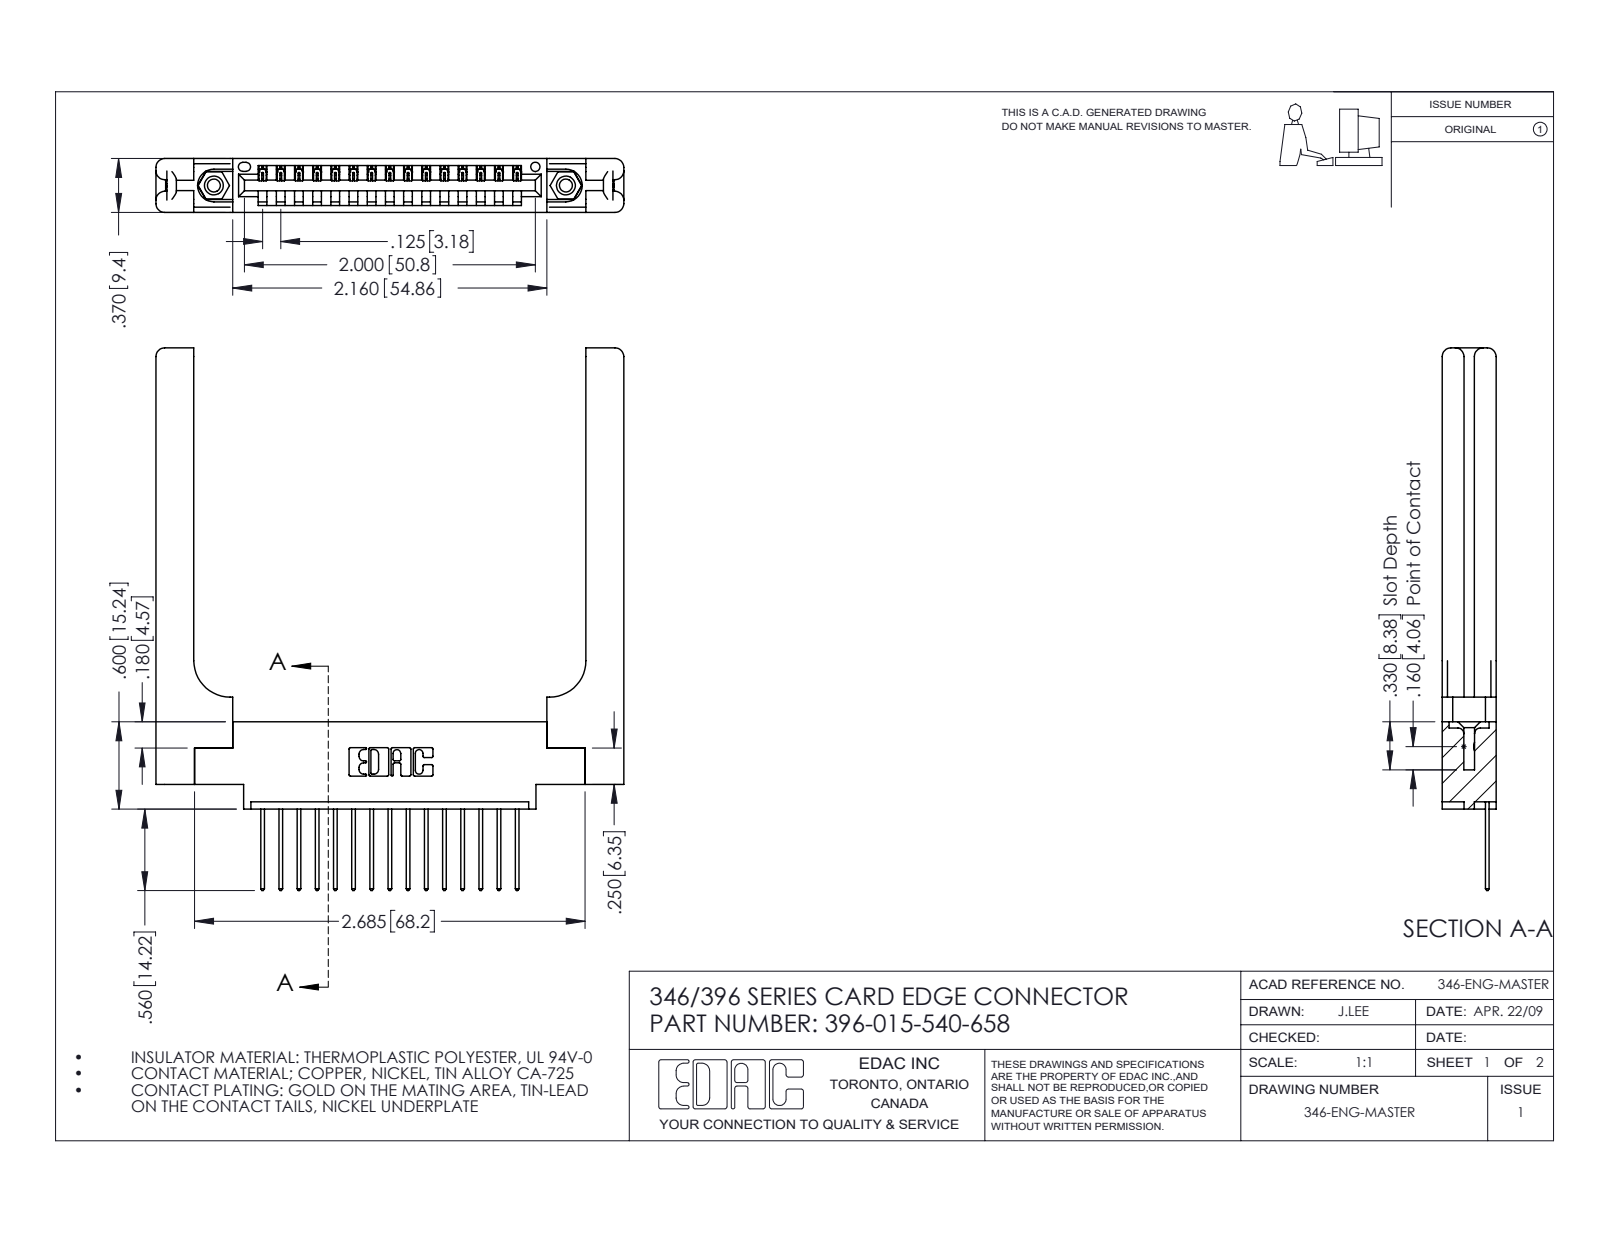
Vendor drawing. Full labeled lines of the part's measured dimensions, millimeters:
Part name (STEP PRODUCT): 345-250-001_345-250-001-102; 345-292-001_345-293-140; 346 Part_0.170 Offset - 0.156 Dia-TH; 396-015-540-658 (+1 more)
STEP written by: SolidWorks 2016 (CONFIG_CONTROL_DESIGN)
Units: millimetres
Bodies: 20 solids, 1252 faces (828 planar, 364 cylindrical, 60 other)
Overall size (bounding box): 94.7 × 81.7 × 9.4
Volume: 15 000 mm³ · Surface area: 14 560 mm²
Round holes (diameter × count): ⌀2.3 ×2, ⌀3.2 ×2, ⌀4 ×2, ⌀1.6 ×1
Round bosses / shafts (diameter × count): ⌀3.9 ×2
Partial cylindrical surfaces — rounded edges, fillets, slot ends (radius × count): R0.2 ×30, R0.3 ×30, R0.3 ×22, R1.5 ×16, R0.2 ×6, R0.8 ×6, R0.7 ×3, R0.8 ×2
Main face-to-face distances: 9.4, 3.8, 1.8, 3.8, 1.2, 8.2, 6.4, 5.6, 2.6, 4.4
Hole centre spacings: 6.2, 56.2, 61.5
